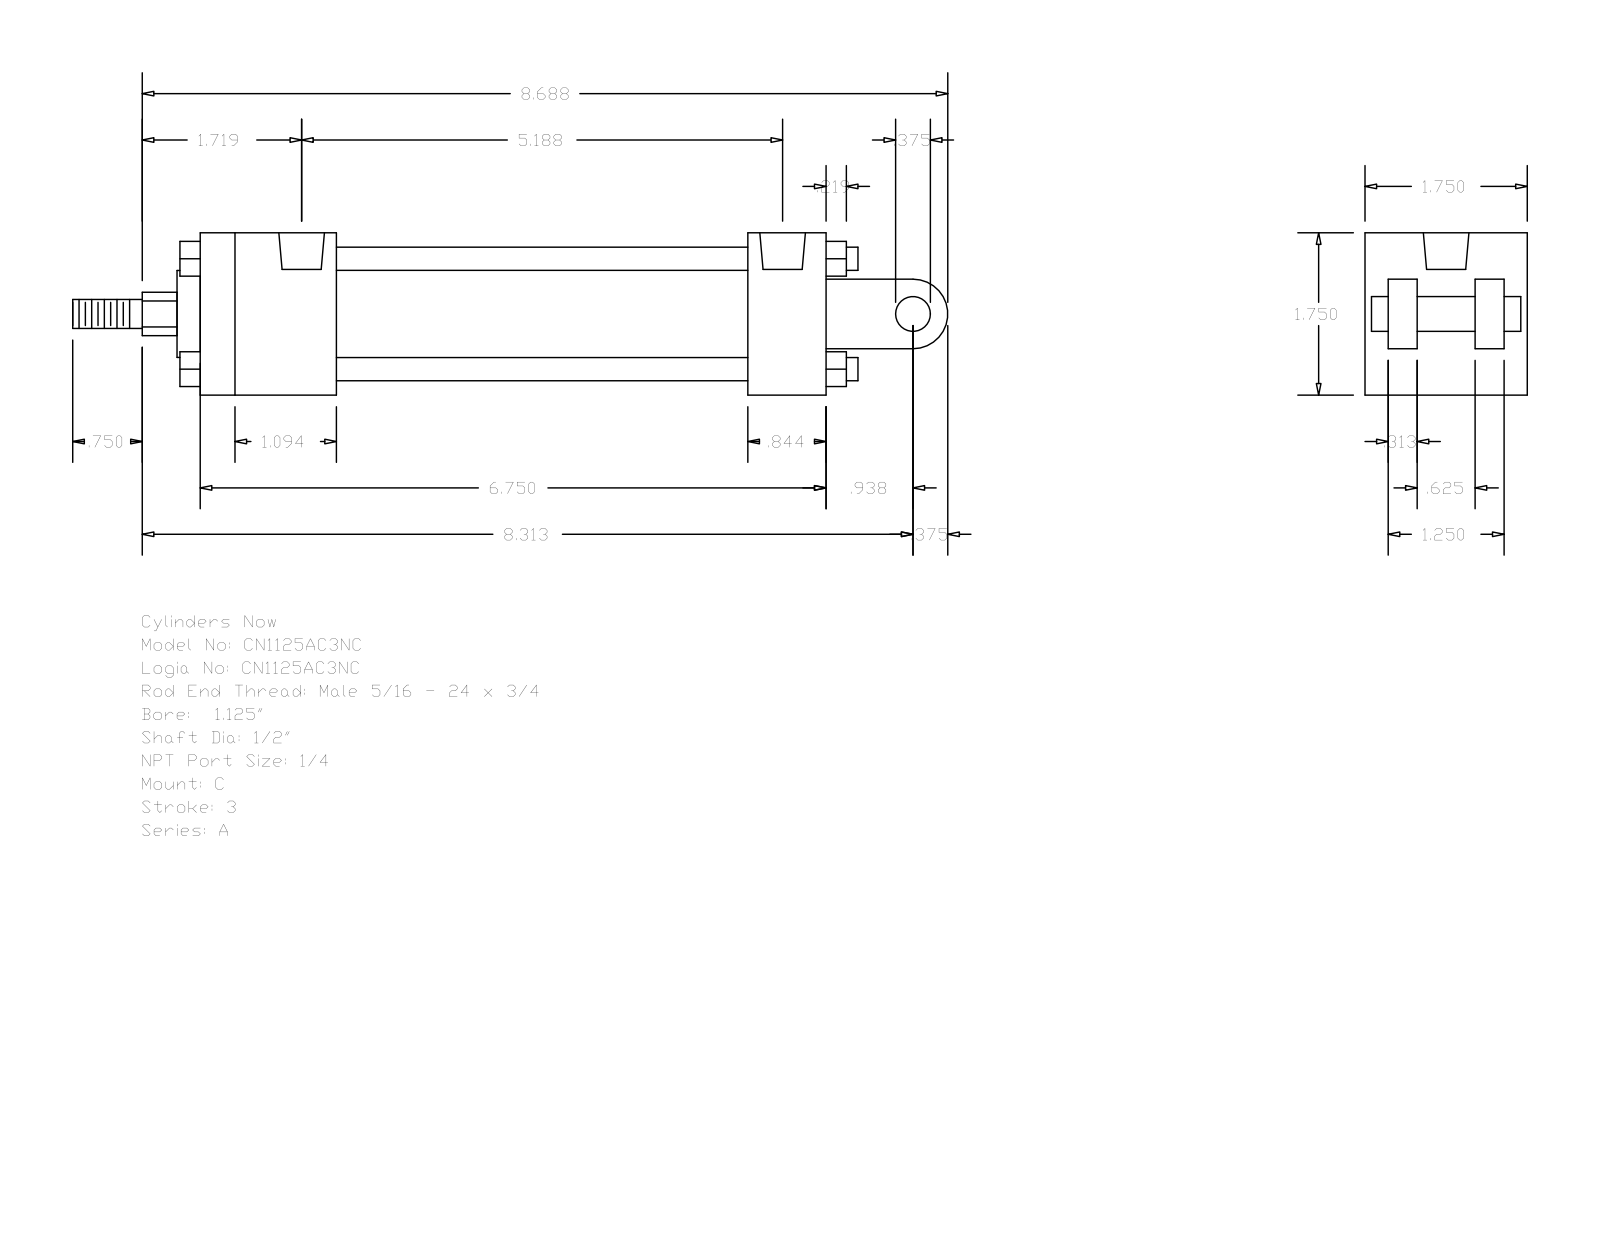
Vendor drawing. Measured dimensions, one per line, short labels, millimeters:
name: A_C__0112_0.5
written by: GSSL Pune (CONFIG_CONTROL_DESIGN)
unit: mm
bodies: 0 solids, 135 faces (102 planar, 33 cylindrical, 0 other)
size: 239.71 × 44.45 × 44.45
holes: 4× ⌀5.56, 2× ⌀12.49
bosses: 4× ⌀6.35, 1× ⌀31.88, 1× ⌀23.81, 1× ⌀12.7, 1× ⌀9.53, 1× ⌀7.94
rounds: 1× R5.94, 1× R9.53
face distances: 44.46, 6.35, 31.76, 14.29, 171.44, 30.17, 150.01, 21.43, 37.3, 112.71
hole spacings: 128.59, 1.58, 1.59, 130.17, 130.18, 131.76
